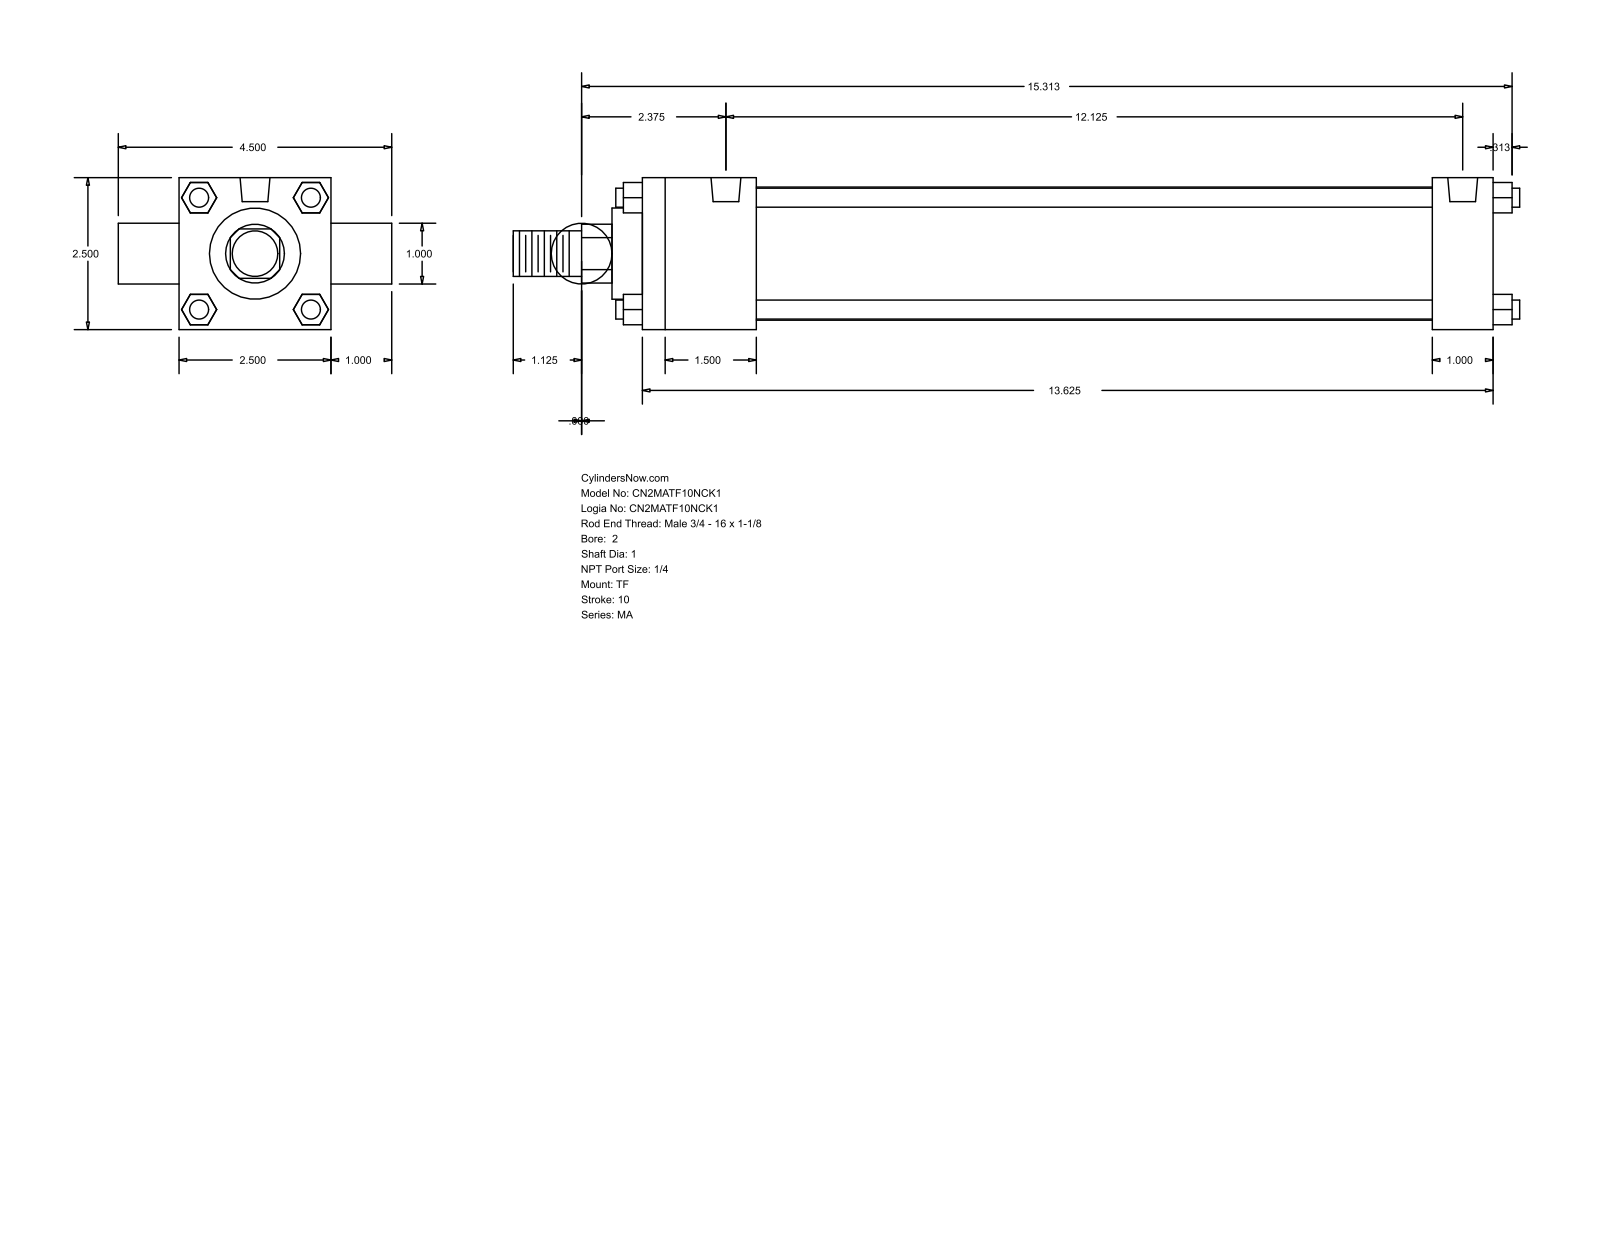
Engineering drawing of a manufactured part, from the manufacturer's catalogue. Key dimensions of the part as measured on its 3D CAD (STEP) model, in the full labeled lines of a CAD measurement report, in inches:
Part name (STEP PRODUCT): MA_TF__0200_1
STEP written by: GSSL Pune (CONFIG_CONTROL_DESIGN)
Units: inches
Bodies: 0 solids, 120 faces (92 planar, 28 cylindrical, 0 other)
Overall size (bounding box): 16.563 × 4.5 × 2.5
Round holes (diameter × count): ⌀0.313 ×3, ⌀0.492 ×2
Round bosses / shafts (diameter × count): ⌀0.313 ×4, ⌀1 ×2, ⌀2.19 ×1, ⌀1.5 ×1, ⌀0.75 ×1
Partial cylindrical surfaces — rounded edges, fillets, slot ends (radius × count): R0.484 ×1
Main face-to-face distances: 2.5, 1, 14, 0.5, 1.875, 13, 11.125, 12.125, 3.5, 0.92
Hole centre spacings: 12.125
